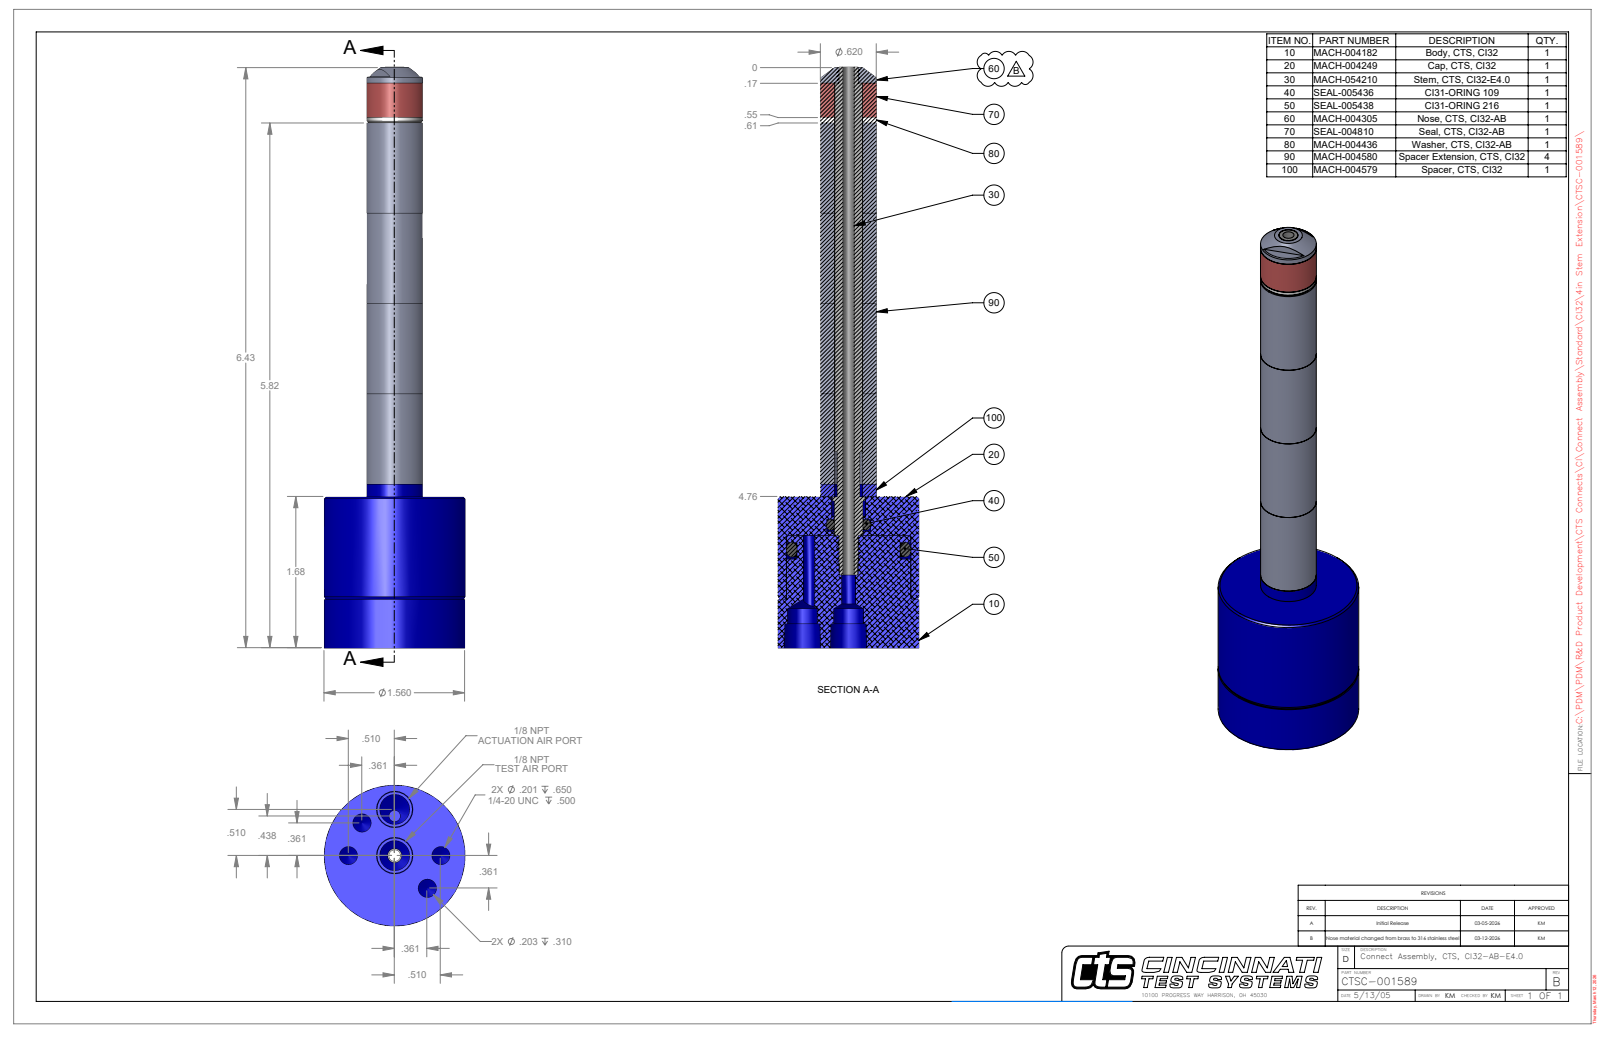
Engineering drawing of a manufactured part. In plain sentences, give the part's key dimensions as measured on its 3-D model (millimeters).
The part is named "CTSC-001589". Its 3-D file was written by "SolidWorks 2023 (AUTOMOTIVE_DESIGN)". It is 9 solids with 83 faces: 37 planar, 31 cylindrical and 15 other. Overall it measures 163.5 by 39.62 by 39.62 millimeters. Its volume is 71 424 cubic millimeters and its surface area 24 801 square millimeters. Round holes: 2 of diameter 3.17, 2 of diameter 5.11, 2 of diameter 5.16, 2 of diameter 8.43, 1 of diameter 3.97, 1 of diameter 5.41, 1 of diameter 7.87, 1 of diameter 7.99, 1 of diameter 9.65. Round bosses or shafts: 1 of diameter 39.62, 1 of diameter 15.75, 1 of diameter 15.7, 1 of diameter 9.08, 1 of diameter 7.72, 1 of diameter 6.35. The main face-to-face distances are 25.4, 42.6, 50.8, 76.2, 158.97, 116.37, 149.32, 106.72, 9.65, 96.99. The hole center spacings are 12.95, 9.91, 23.93, 17.06, 18.31, 1.84, 9.37, 11.11.
